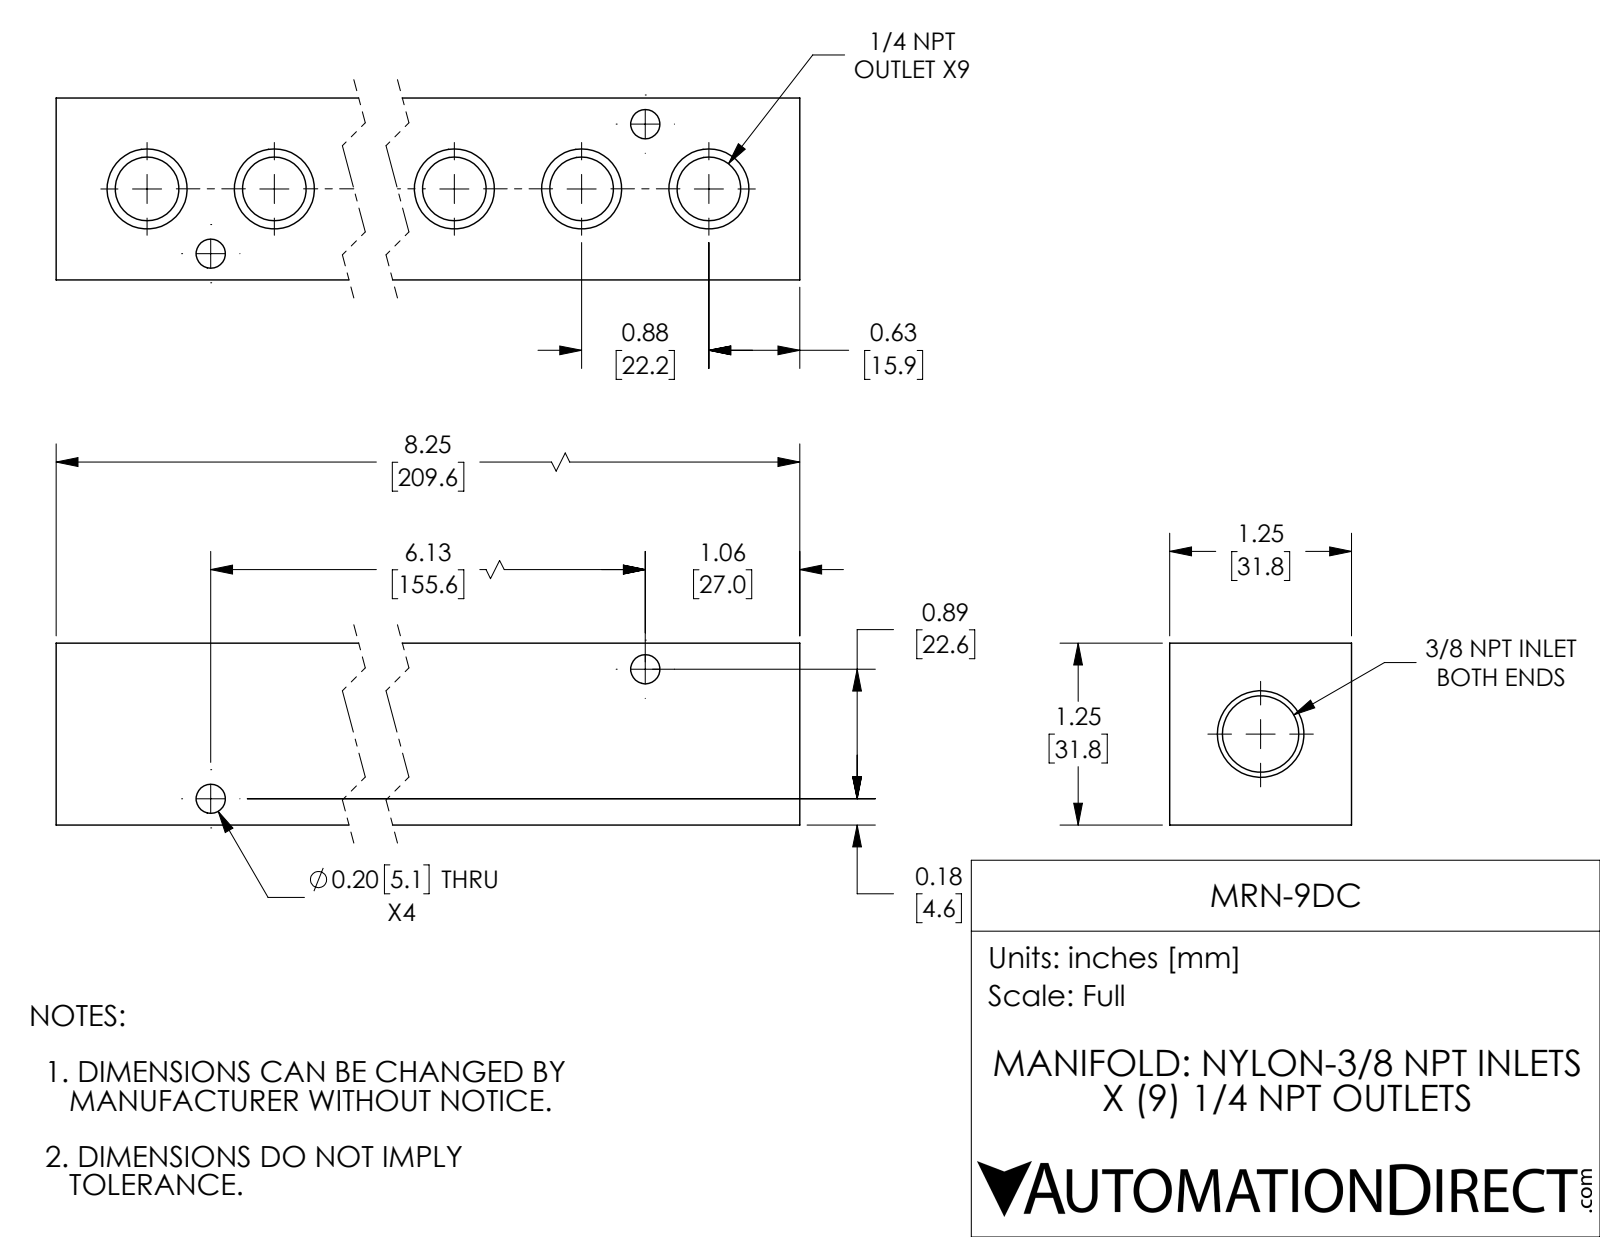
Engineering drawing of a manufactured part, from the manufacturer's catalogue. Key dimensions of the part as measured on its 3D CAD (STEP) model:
Part name (STEP PRODUCT): MRN-9DC
STEP written by: SolidWorks 2018 (AUTOMOTIVE_DESIGN)
Units: inches
Bodies: 1 solid, 64 faces (6 planar, 36 cylindrical, 22 other)
Overall size (bounding box): 8.25 × 1.25 × 1.25
Volume: 10.41 in³ · Surface area: 61.98 in²
Round holes (diameter × count): ⌀0.438 ×9, ⌀0.201 ×4, ⌀0.525 ×1
Main face-to-face distances: 1.25, 8.25
Hole centre spacings: 1.75, 0.875, 0.624, 2.625, 3.5, 0.875, 4.375, 2.232
